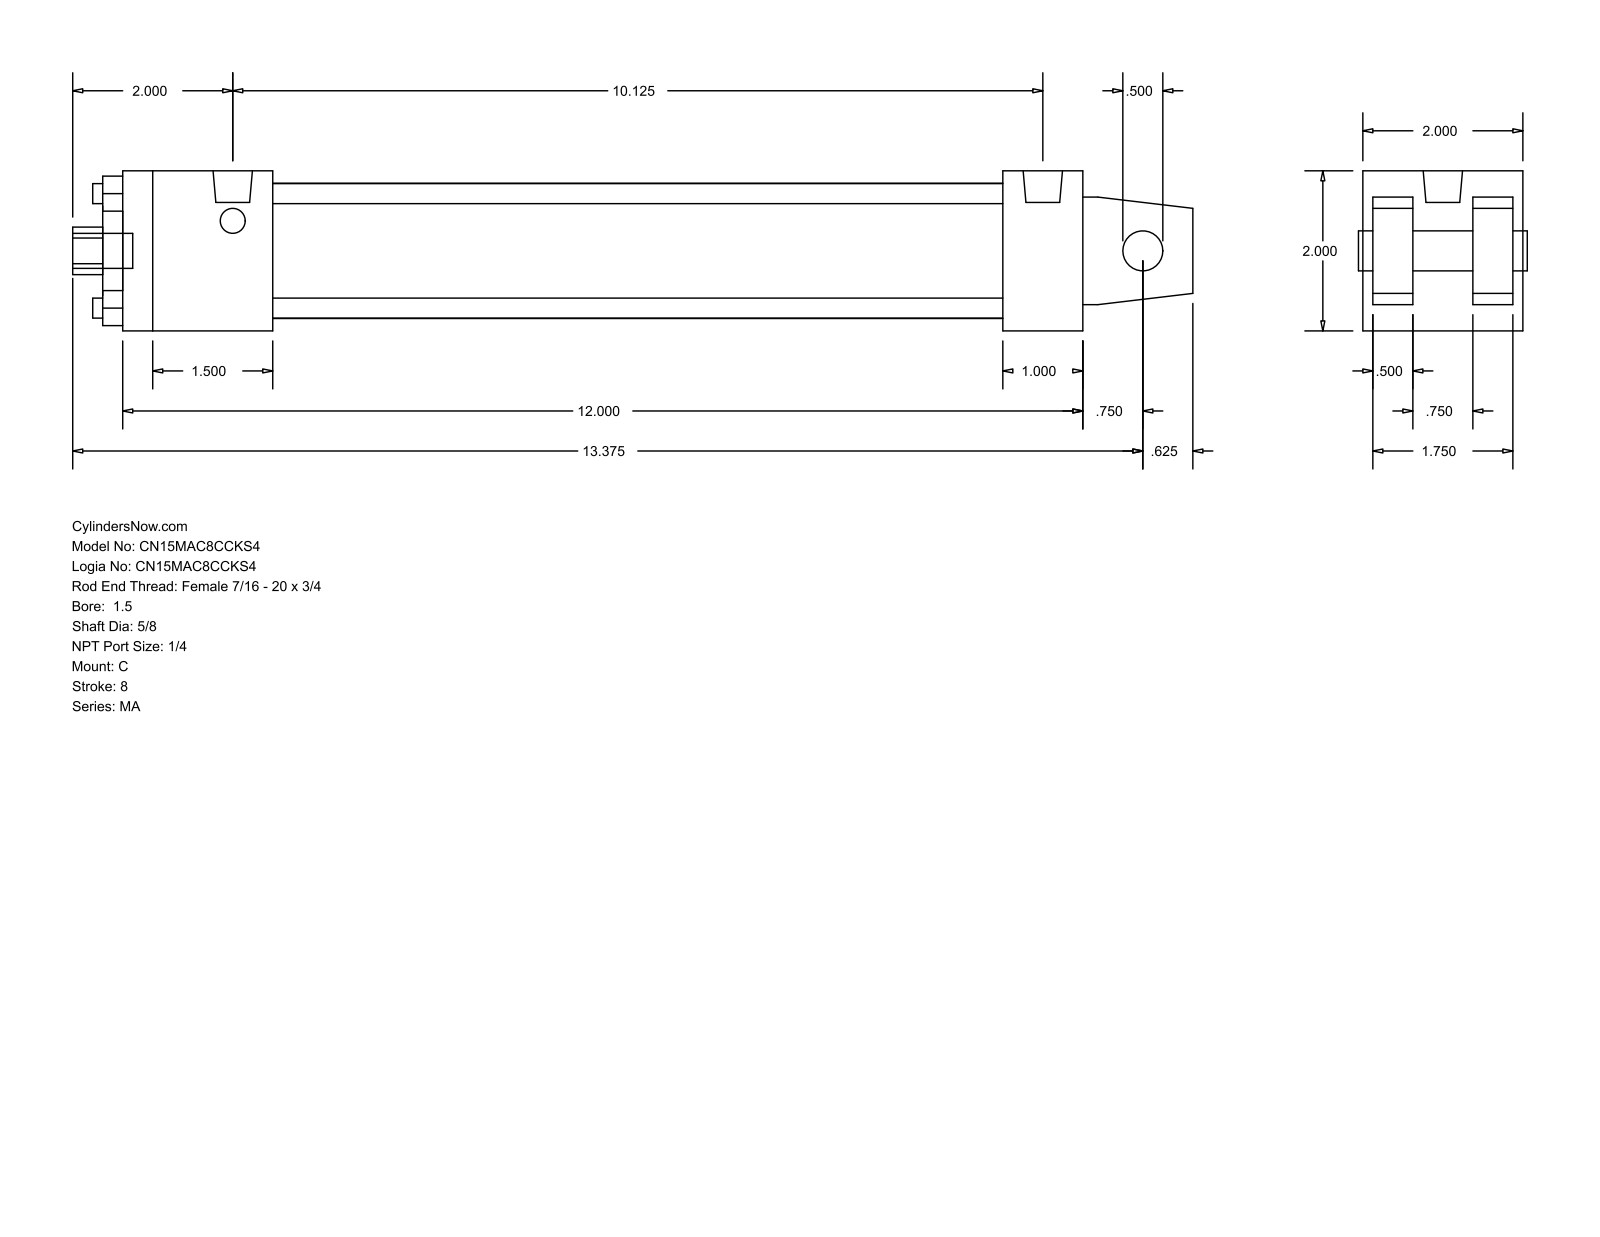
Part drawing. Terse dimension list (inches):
name: MA_C__0150_0.625
written by: GSSL Pune (CONFIG_CONTROL_DESIGN)
unit: in
bodies: 0 solids, 103 faces (76 planar, 27 cylindrical, 0 other)
size: 14 × 2 × 2
holes: 4× ⌀0.25, 1× ⌀0.5, 1× ⌀0.625, 1× ⌀1.125, 1× ⌀1.69
bosses: 4× ⌀0.313, 2× ⌀0.492, 1× ⌀0.437
rounds: 1× R0.297
face distances: 2, 0.5, 0.125, 0.625, 1.375, 1.875, 1.25, 12, 11, 1
hole spacings: 1.011, 1.43, 2.022
